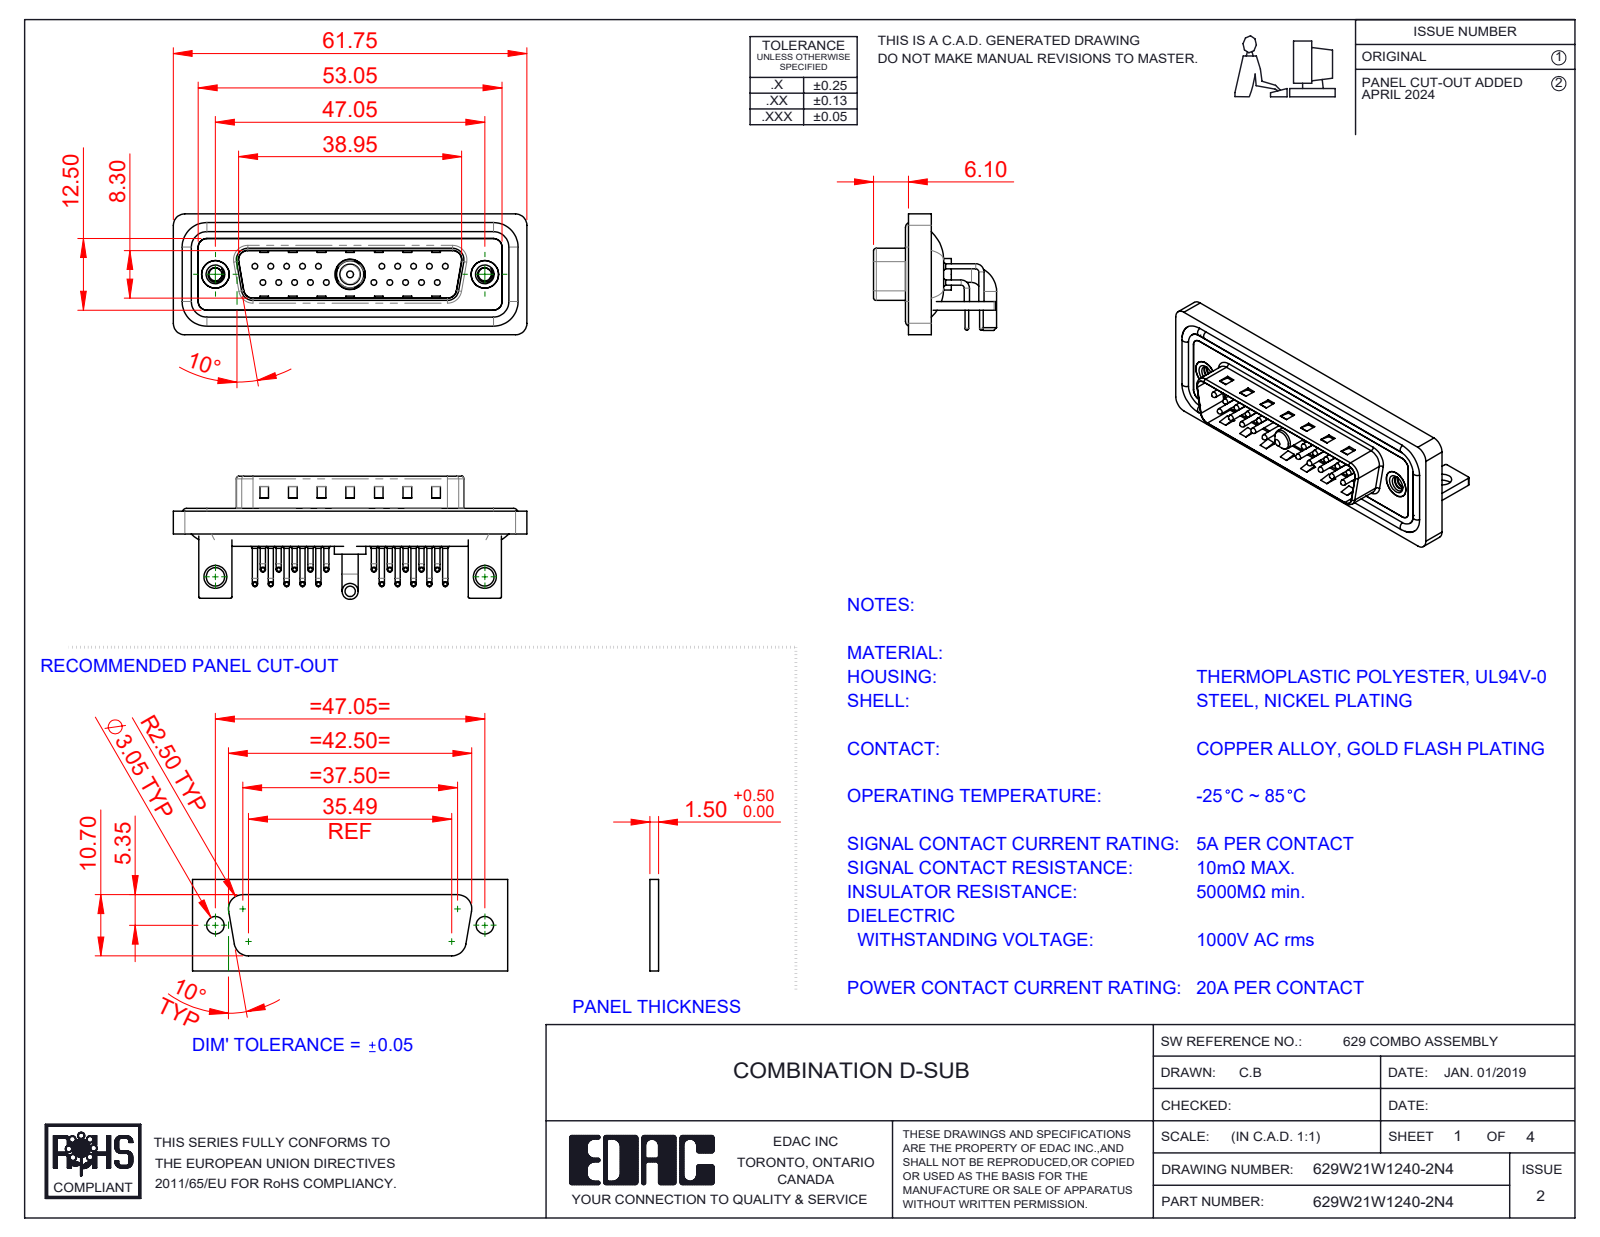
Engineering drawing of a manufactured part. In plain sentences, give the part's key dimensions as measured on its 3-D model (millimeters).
The part is named "629Combo Stabilizer Bracket; 629Combo Contact Row 2; 629Combo Shell Rear_25 Contacts; 629W21W1140-2N4 (+6 more)". Its 3-D file was written by "SolidWorks 2023 (CONFIG_CONTROL_DESIGN)". It is 31 solids with 2766 faces: 1519 planar, 947 cylindrical and 300 other. Overall it measures 61.75 by 21.5 by 21.1 millimeters. Its volume is 7 695 cubic millimeters and its surface area 13 308 square millimeters. Round holes: 20 of diameter 0.75, 20 of diameter 1.6, 20 of diameter 2, 2 of diameter 2.26, 2 of diameter 3.2, 2 of diameter 4, 2 of diameter 4.8, 2 of diameter 5, 1 of diameter 4.85, 1 of diameter 5.3. Round bosses or shafts: 40 of diameter 0.9, 20 of diameter 1.5, 20 of diameter 1, 20 of diameter 0.65, 4 of diameter 1.6, 2 of diameter 4.9, 2 of diameter 2.8, 1 of diameter 5.5. Partial cylindrical surfaces (rounded edges, fillets, slot ends): 20 of radius 1.01, 19 of radius 2, 18 of radius 1.5, 16 of radius 0.25, 9 of radius 0.5, 8 of radius 1.6, 4 of radius 0.6, 4 of radius 0.65. The main face-to-face distances are 0.4, 0.8, 2.1, 2.9, 1.5, 1.1, 4.1, 1.6, 4.5, 3.7. The hole center spacings are 3.16, 2.77, 5.54, 8.31, 5.04, 19.39, 20.97, 22.16.
